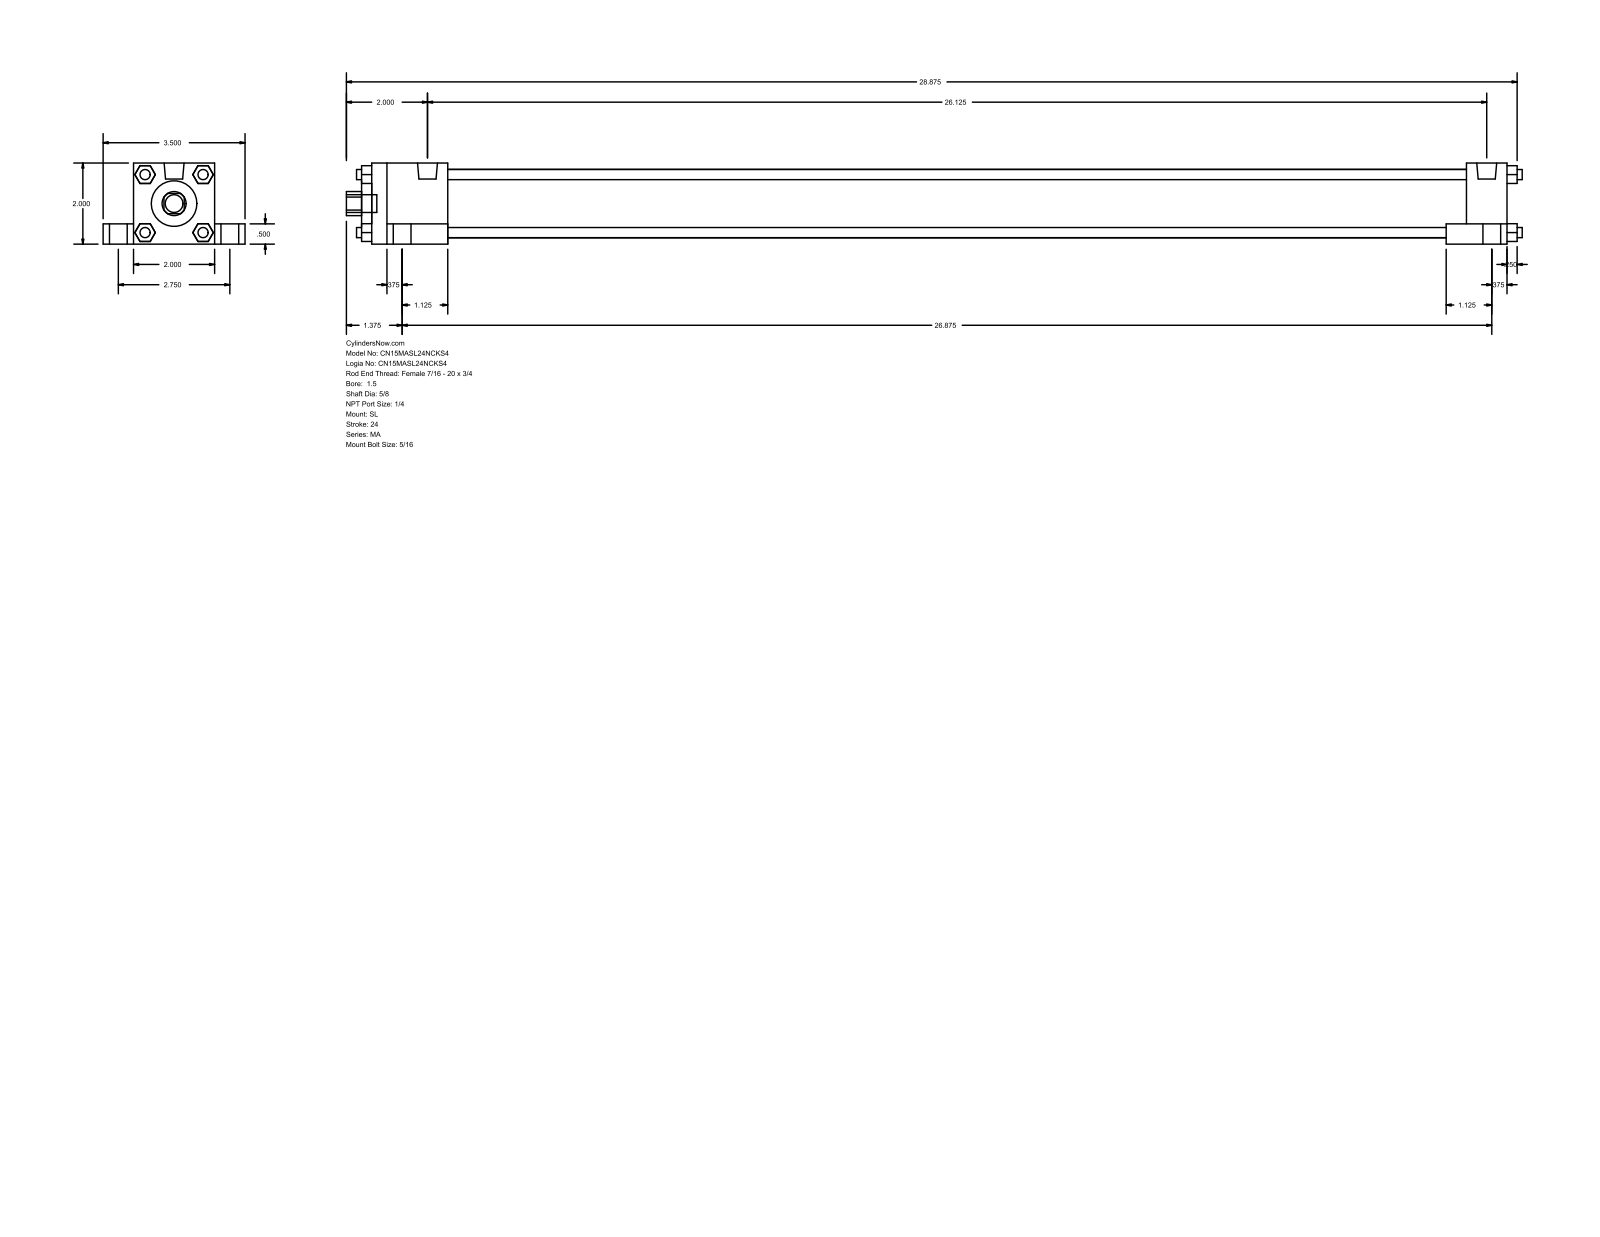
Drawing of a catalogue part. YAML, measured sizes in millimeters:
part_name: "MA_SL__0150_0.625"
step_written_by: "GSSL Pune (CONFIG_CONTROL_DESIGN)"
units: millimeters
bodies: {solids: 0, faces: 148, planar: 112, cylindrical: 36, other: 0}
overall_size: [736.6, 88.9, 50.8]
round_holes:
  - {diameter: 15.88, count: 1}
  - {diameter: 28.57, count: 1}
  - {diameter: 42.93, count: 1}
round_bosses_or_shafts:
  - {diameter: 11.11, count: 5}
  - {diameter: 17.46, count: 4}
  - {diameter: 7.94, count: 4}
  - {diameter: 6.35, count: 4}
  - {diameter: 12.49, count: 2}
partial_cylinders:
  - {radius: 7.54, count: 1}
face_to_face_distances: [50.8, 19.05, 38.1, 12.7, 711.2, 69.85, 638.17, 9.52, 685.79, 25.41]
